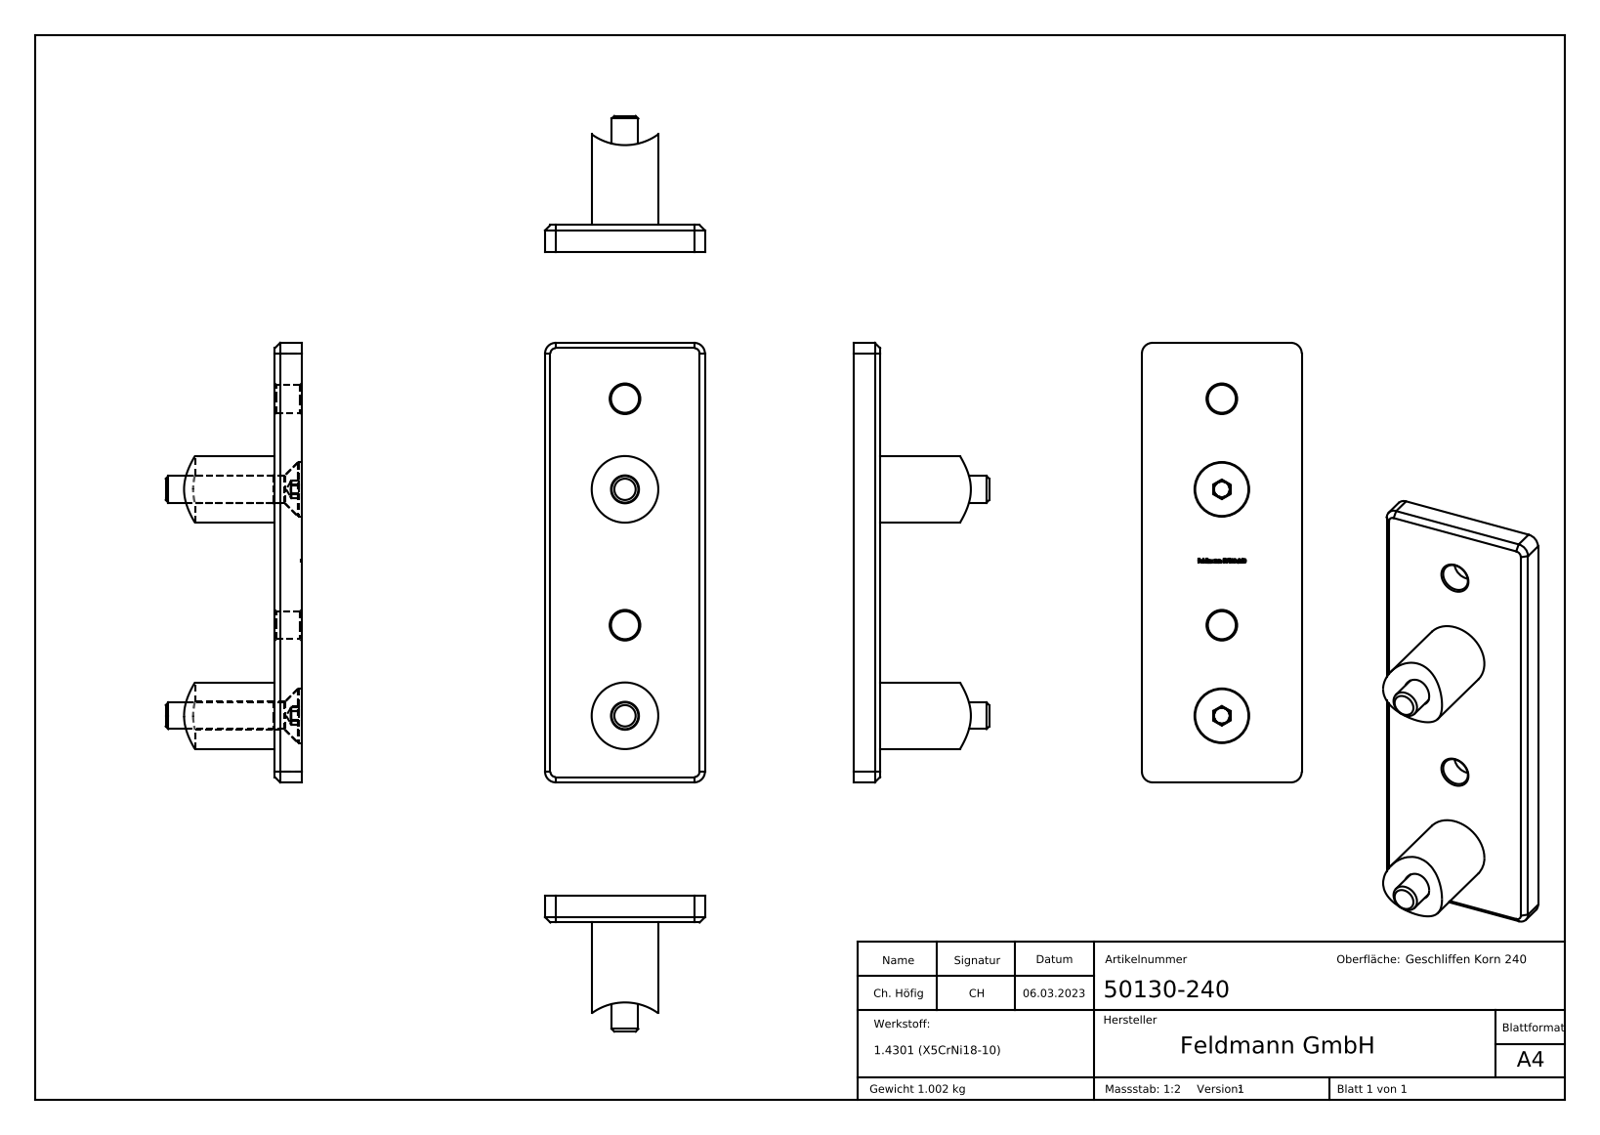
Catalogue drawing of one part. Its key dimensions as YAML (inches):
part_name: "50130-240; 50130-240 Halter_50130-240 Teil2; 50130-240 Platte_50130-240 Teil1; DIN7991 M10x60_DIN7991 M10x50"
step_written_by: "SolidWorks 2018 (CONFIG_CONTROL_DESIGN)"
units: inches
bodies: {solids: 5, faces: 437, planar: 156, cylindrical: 64, other: 217}
overall_size: [6.496, 2.362, 2.006]
volume: 7.743
surface_area: 57.81
round_holes:
  - {diameter: 0.413, count: 4}
  - {diameter: 0.807, count: 2}
round_bosses_or_shafts:
  - {diameter: 0.984, count: 2}
  - {diameter: 0.787, count: 2}
  - {diameter: 0.394, count: 2}
partial_cylinders:
  - {radius: 0.008, count: 31}
  - {radius: 0.157, count: 4}
  - {radius: 0.835, count: 1}
face_to_face_distances: [0.394, 2.362, 0.037, 0.356, 6.496, 2.006, 1.969, 1.612, 1.063, 1.299]
hole_center_spacings: [1.339, 3.346, 2.008, 4.685]
